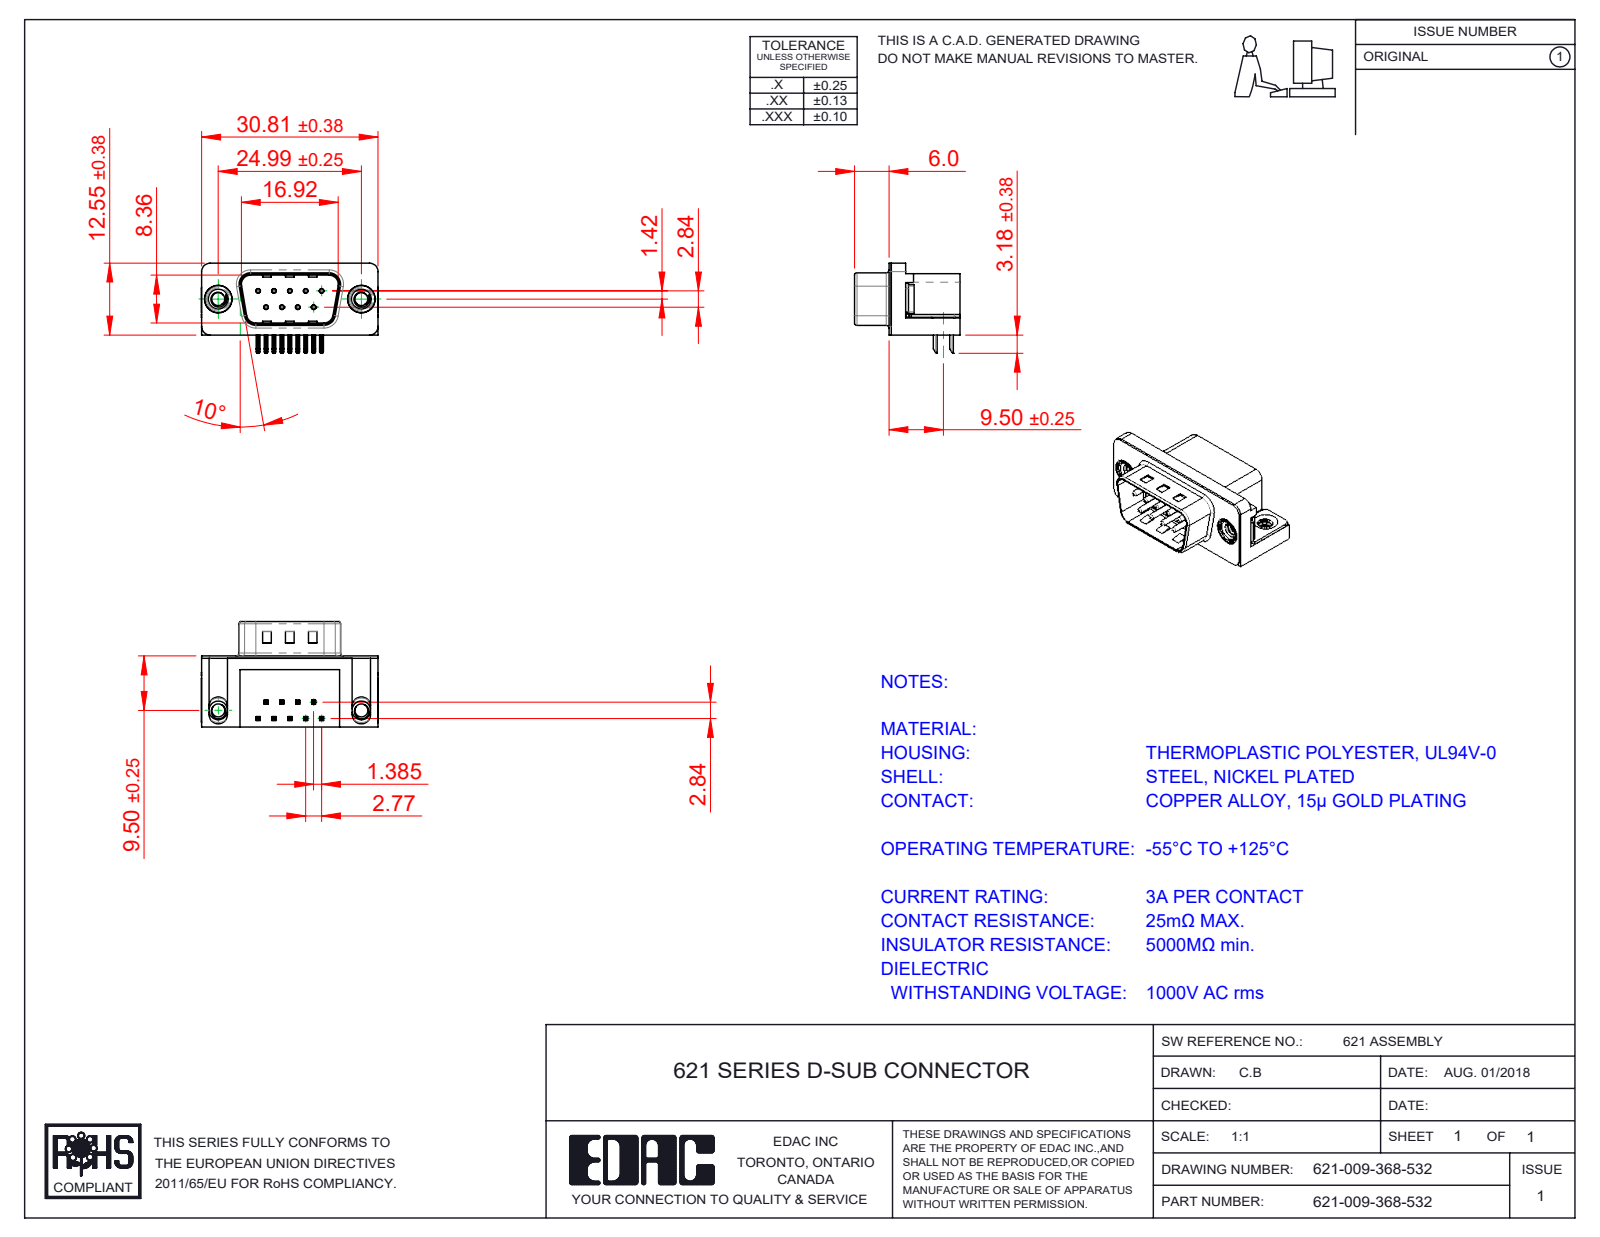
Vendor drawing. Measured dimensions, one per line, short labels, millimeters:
name: 621 Housing_9 Socket; 621 Contact Bottom; 621-009-368-532; 621 4-40 Threaded Rivet (+3 more)
written by: SolidWorks 2016 (CONFIG_CONTROL_DESIGN)
unit: mm
bodies: 15 solids, 1031 faces (605 planar, 323 cylindrical, 103 other)
size: 30.89 × 18.4 × 16.25
volume: 3 246 mm³; area: 4 427 mm²
holes: 9× ⌀0.35, 9× ⌀0.8, 2× ⌀2.26, 2× ⌀4, 2× ⌀4.8, 2× ⌀5
bosses: 9× ⌀0.75, 2× ⌀4.9, 2× ⌀4.75, 2× ⌀3.9
rounds: 44× R0.25, 18× R0.12, 16× R1, 14× R0.5, 8× R1.5, 8× R1.6, 4× R0.32, 4× R0.9
face distances: 0.4, 12, 12.4, 10.35, 0.5, 9.5, 2.5, 2.9, 2.1, 0.35
hole spacings: 3.16, 2.77, 5.54, 5.03, 5.04, 8.31, 7.48, 7.49
